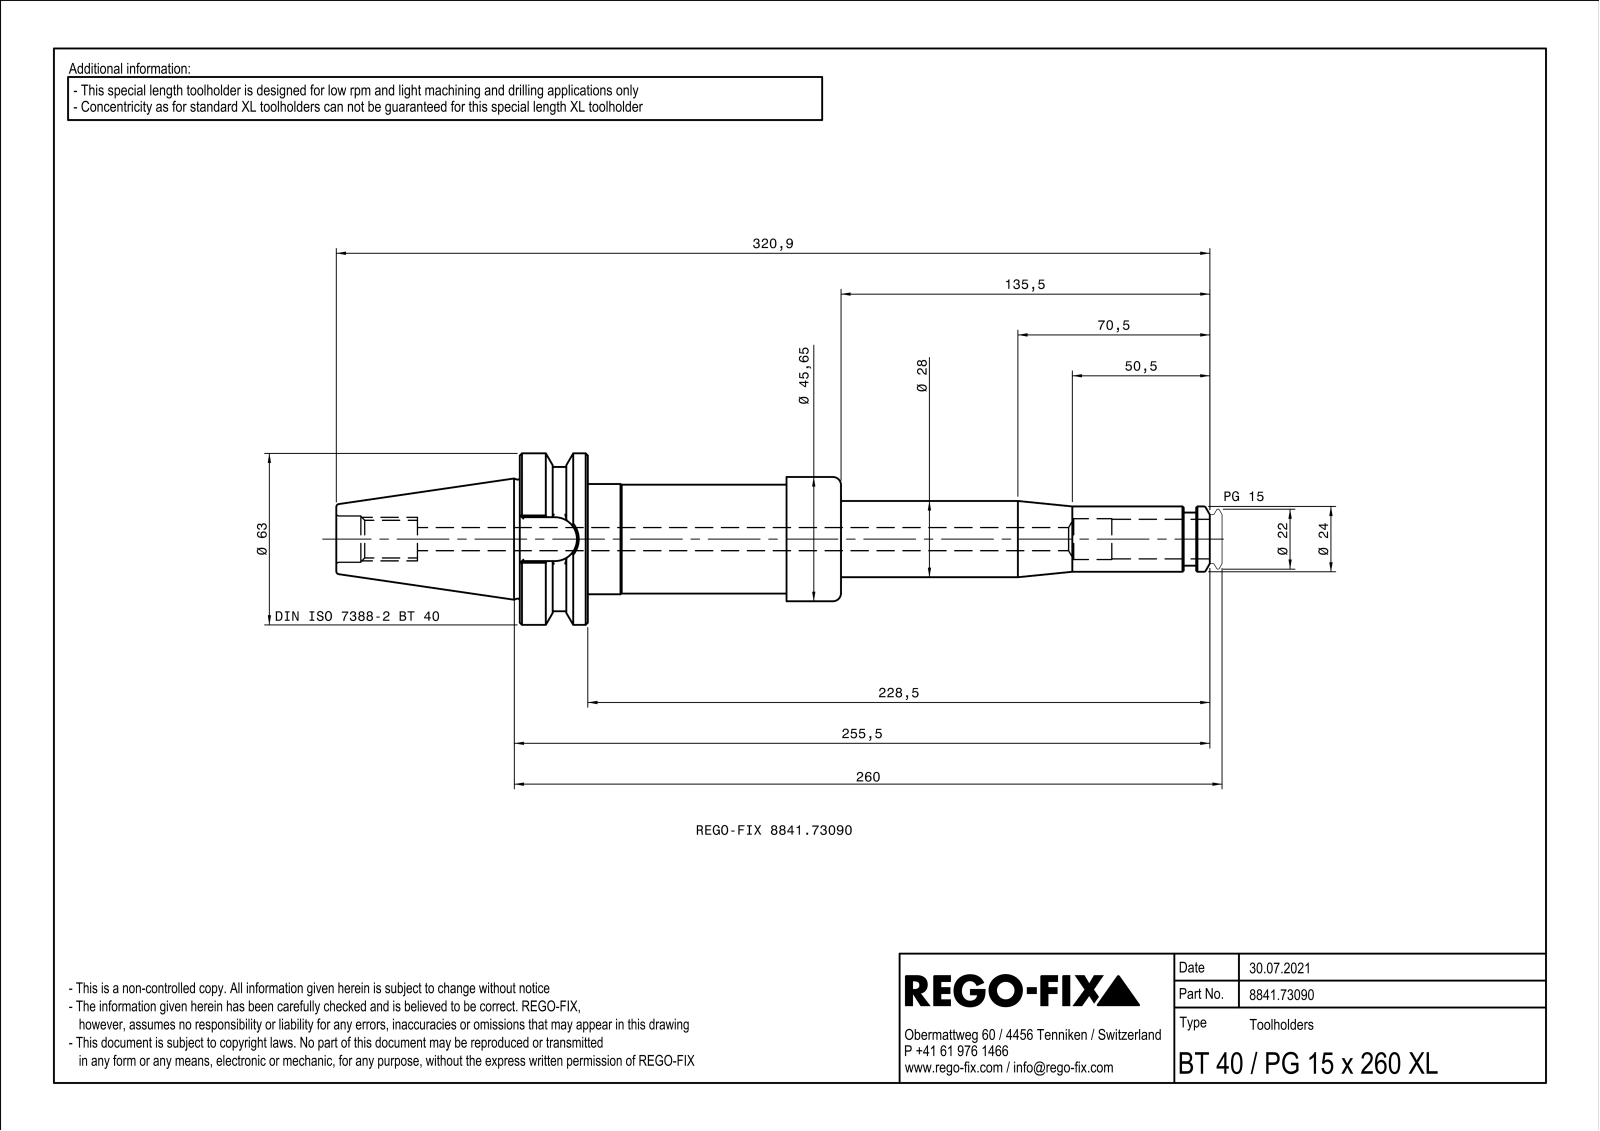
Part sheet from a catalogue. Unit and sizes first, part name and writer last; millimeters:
Units: millimetres
Overall size (bounding box): 320.9 × 63 × 63
Round holes (diameter × count): ⌀9 ×1, ⌀10 ×1, ⌀13 ×1, ⌀13.84 ×1, ⌀15 ×1, ⌀17 ×1, ⌀25 ×1, ⌀29 ×1, ⌀38.38 ×1, ⌀40.05 ×1, ⌀43.3 ×1
Round bosses / shafts (diameter × count): ⌀63 ×1, ⌀53 ×1, ⌀45.65 ×1, ⌀40.5 ×1, ⌀40 ×1, ⌀34 ×1, ⌀33 ×1, ⌀28 ×1
Partial cylindrical surfaces — rounded edges, fillets, slot ends (radius × count): R0.5 ×4, R8.05 ×1, R22.77 ×1
Main face-to-face distances: 25, 93, 118, 6, 14, 1.5, 91.5, 116.5, 20, 18.5
Volume: 281 491 mm³ · Surface area: 62 102 mm²
Bodies: 1 solid, 151 faces (52 planar, 35 cylindrical, 64 other)
Part name (STEP PRODUCT): NOCUT
STEP written by: SIEMENS PLM Software Solid Edge ST10 (AUTOMOTIVE_DESIGN)
